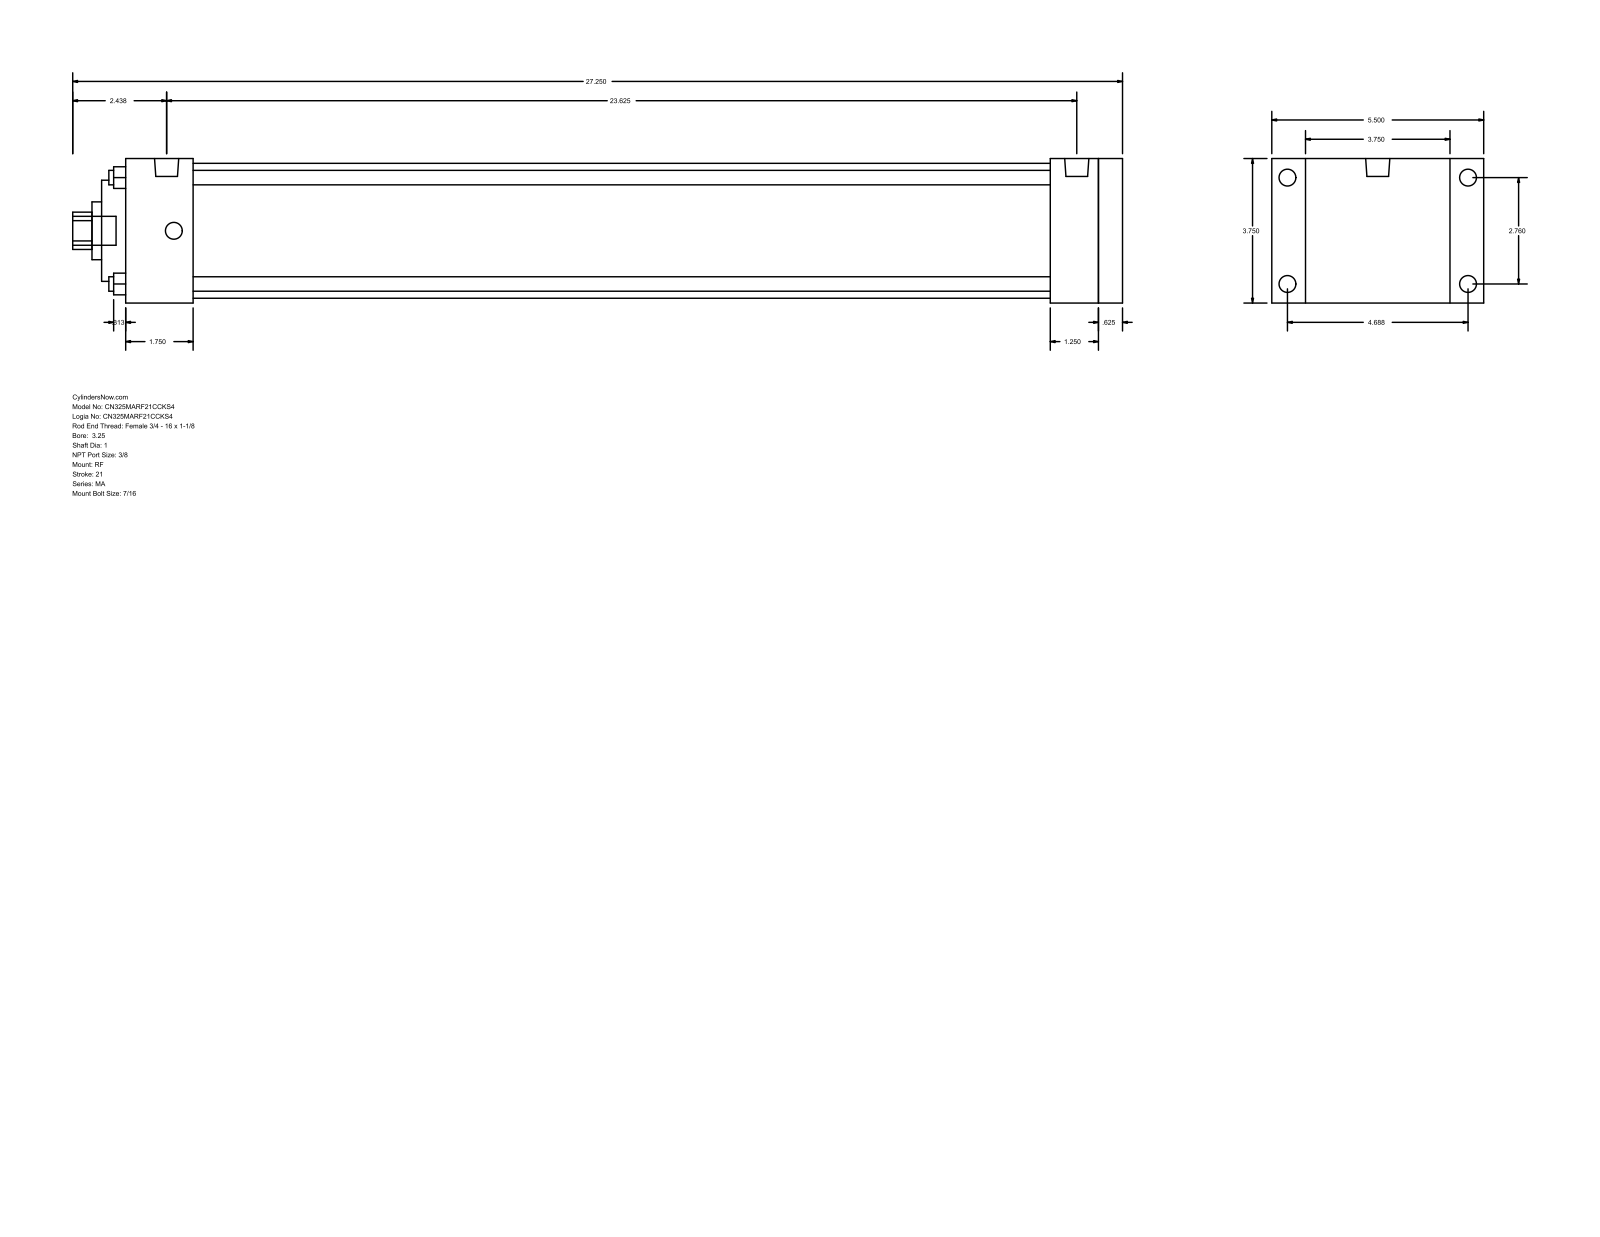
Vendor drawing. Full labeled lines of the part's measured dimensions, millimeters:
Part name (STEP PRODUCT): MA_RF__0325_1
STEP written by: GSSL Pune (CONFIG_CONTROL_DESIGN)
Units: millimetres
Bodies: 0 solids, 94 faces (65 planar, 29 cylindrical, 0 other)
Overall size (bounding box): 692.15 × 139.7 × 95.25
Round holes (diameter × count): ⌀9.53 ×4, ⌀25.4 ×1, ⌀38.1 ×1, ⌀66.67 ×1, ⌀88.9 ×1
Round bosses / shafts (diameter × count): ⌀11.11 ×8, ⌀15.93 ×2, ⌀19.05 ×1
Partial cylindrical surfaces — rounded edges, fillets, slot ends (radius × count): R12.29 ×1
Main face-to-face distances: 95.24, 657.23, 641.35, 15.88, 22.23, 117.47, 15.87, 609.6, 31.75, 47.63
Hole centre spacings: 49.57, 70.1, 99.14
